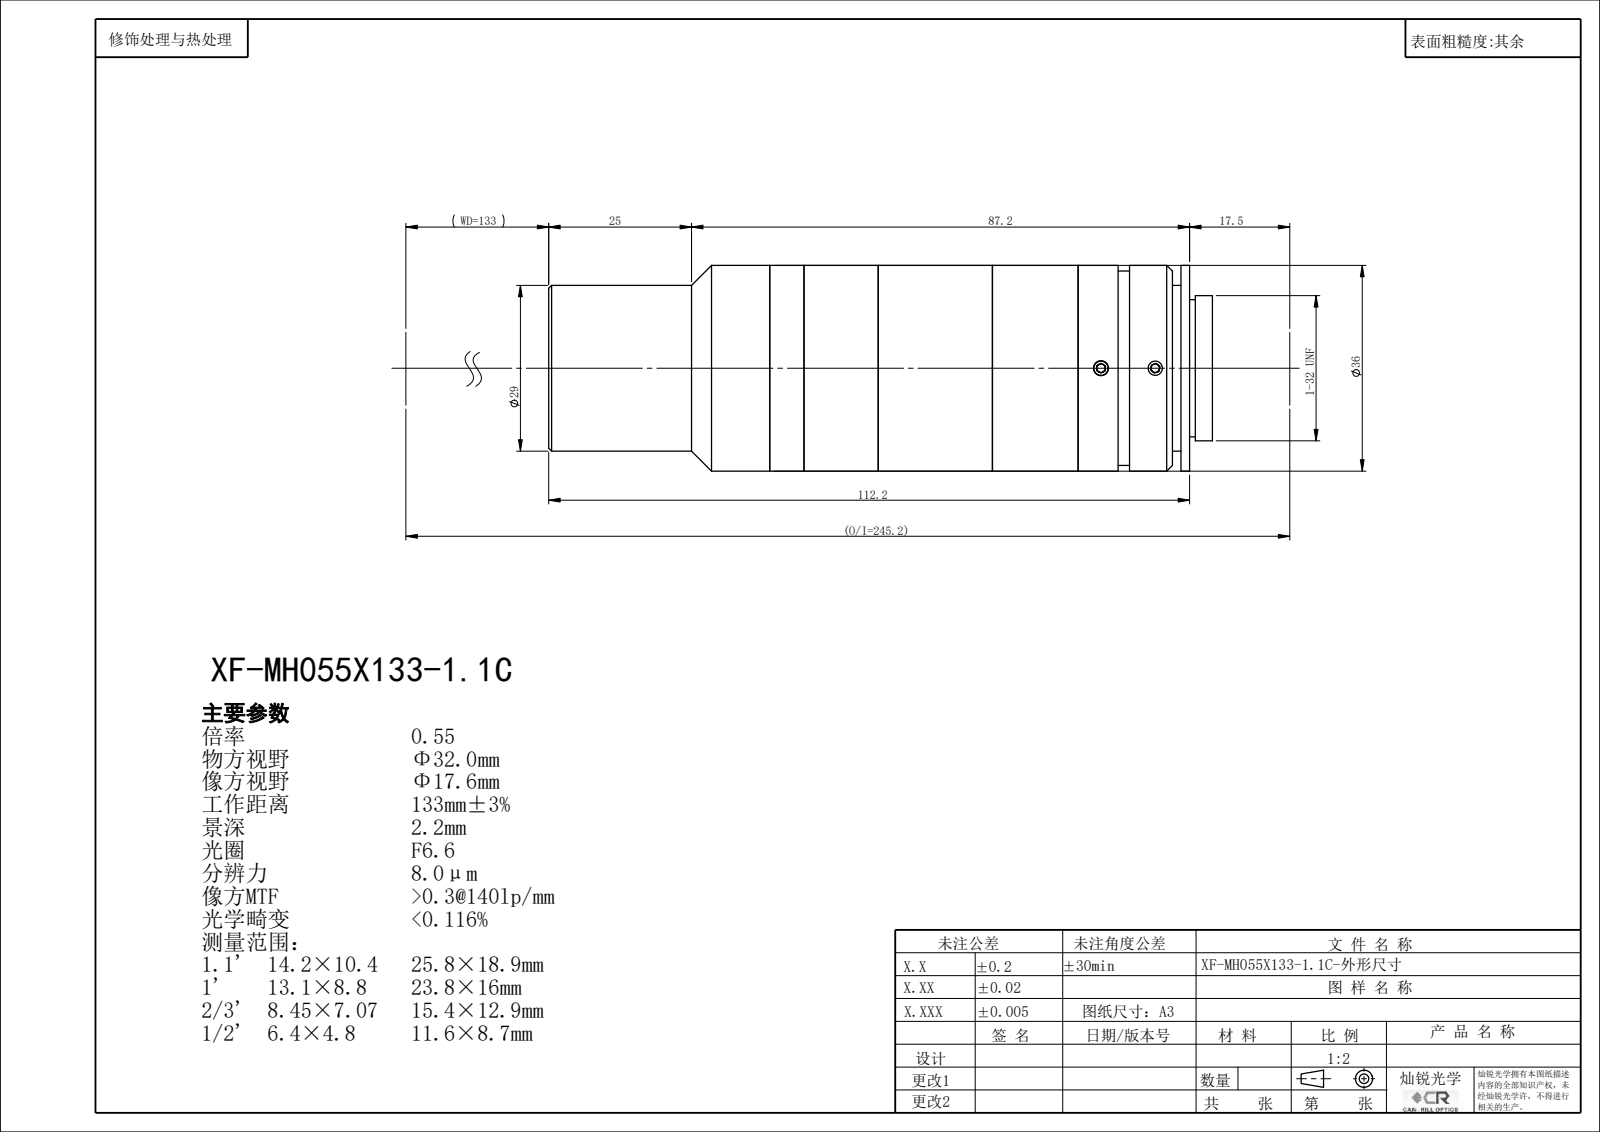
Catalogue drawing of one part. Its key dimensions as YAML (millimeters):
part_name: "XF-MH055X133-1.1C"
step_written_by: "SolidWorks 2022 (CONFIG_CONTROL_DESIGN)"
units: millimeters
bodies: {solids: 0, faces: 135, planar: 69, cylindrical: 44, other: 22}
overall_size: [116.19, 36, 36]
round_holes:
  - {diameter: 2.5, count: 3}
  - {diameter: 20, count: 1}
  - {diameter: 22.4, count: 1}
  - {diameter: 24, count: 1}
  - {diameter: 24.9, count: 1}
  - {diameter: 26, count: 1}
  - {diameter: 26.4, count: 1}
round_bosses_or_shafts:
  - {diameter: 36, count: 1}
  - {diameter: 34, count: 1}
  - {diameter: 29, count: 1}
  - {diameter: 25.4, count: 1}
face_to_face_distances: [19.51, 1.5, 18.01, 15, 33.01, 34.51, 20, 35, 53.01, 54.51]
